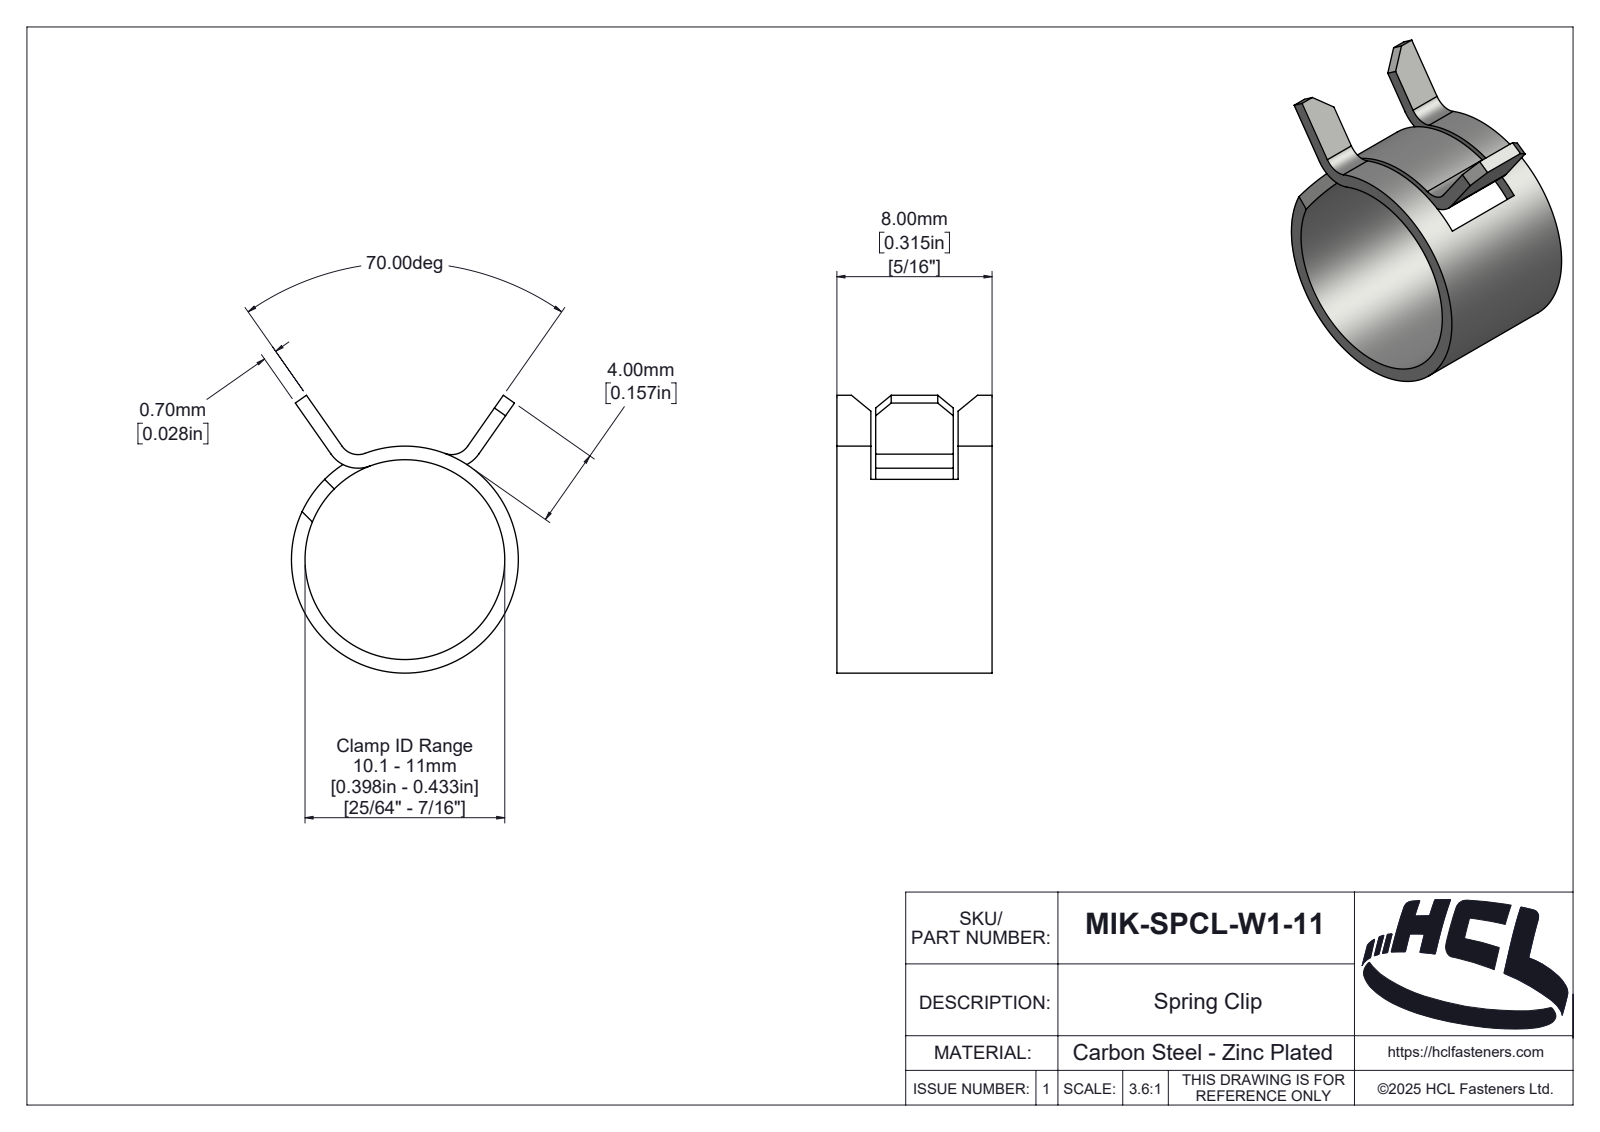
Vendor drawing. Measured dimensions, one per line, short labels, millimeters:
name: MIK-SPCL-W1-11
written by: SolidWorks 2025 (AUTOMOTIVE_DESIGN)
unit: mm
bodies: 1 solid, 135 faces (24 planar, 62 cylindrical, 49 other)
size: 14.32 × 11.7 × 8
volume: 200 mm³; area: 669 mm²
holes: 1× ⌀10.3
bosses: 1× ⌀11.7
rounds: 2× R1, 2× R1.7, 1× R0.23, 1× R0.94, 1× R1.18, 1× R1.24, 1× R1.5, 1× R2.12
face distances: 8, 0.7, 2, 6, 1.75, 6.25, 4.25, 4, 4.5
